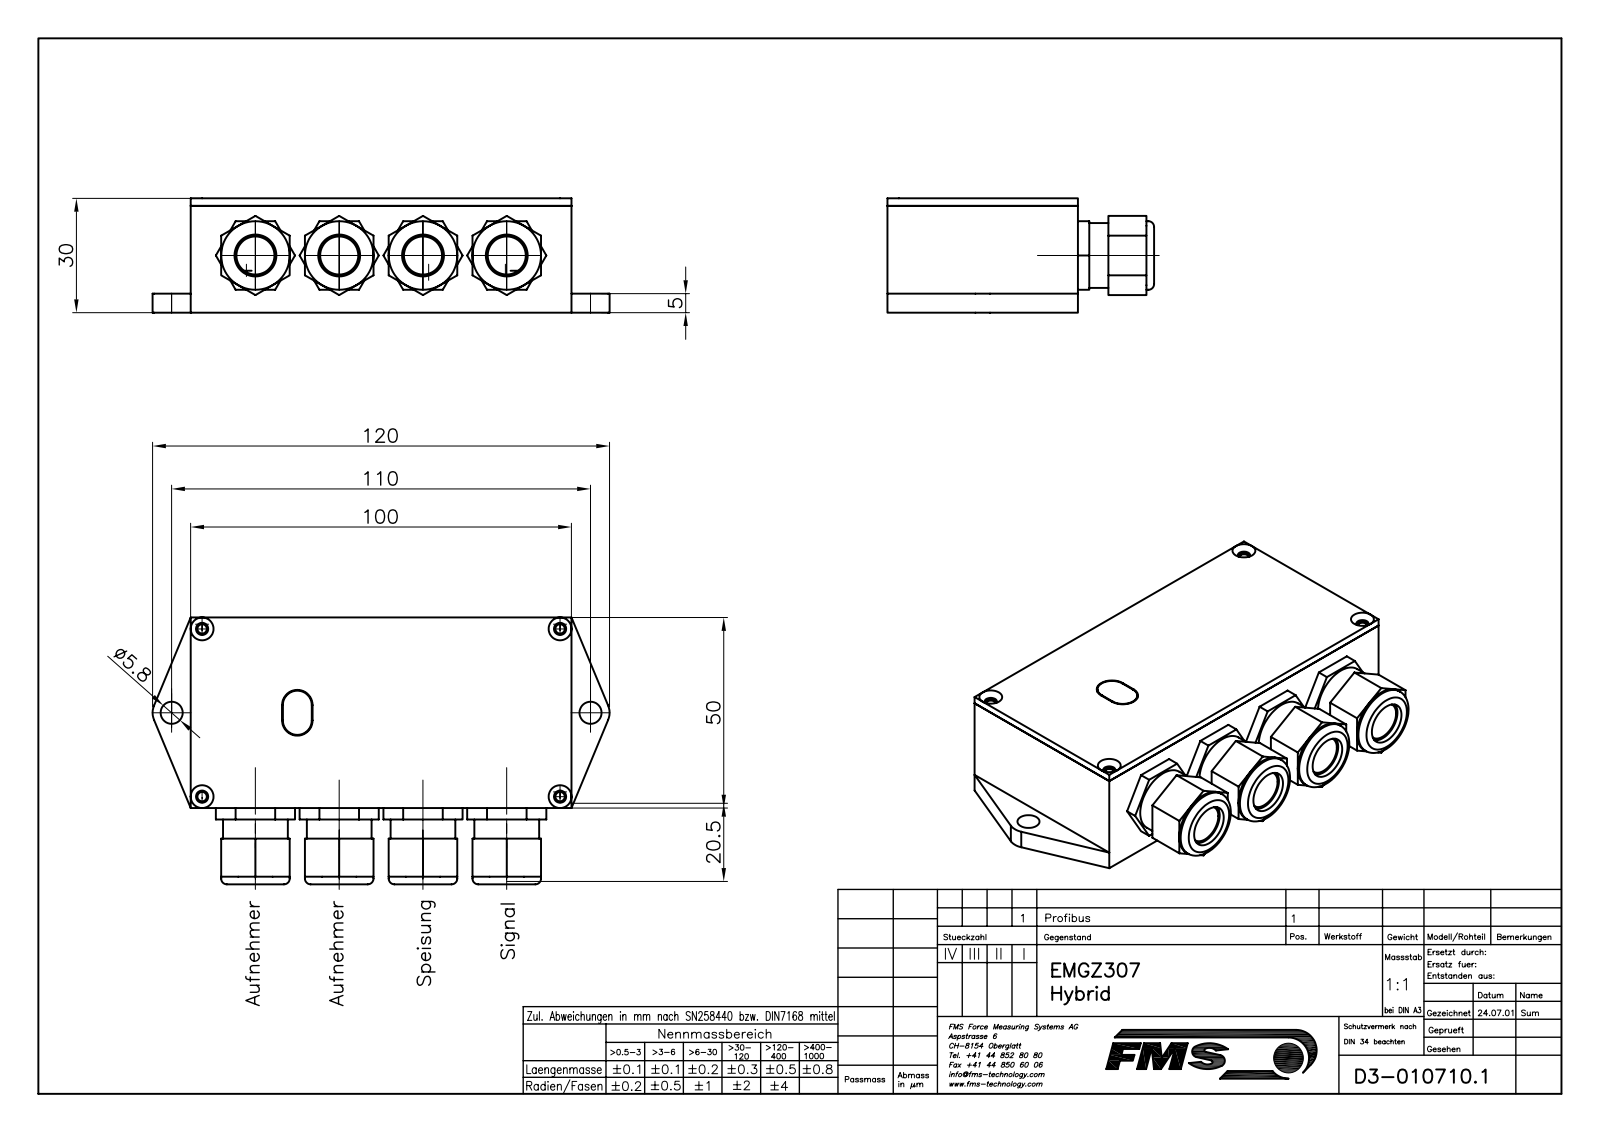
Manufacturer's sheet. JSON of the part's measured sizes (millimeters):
{"part_name": "E0107101; E0107107; E0107102; KABELVERSCHRAUBUNG_M16X1.5 (+8 more)", "step_written_by": "Mechanical Desktop 2009 (CONFIG_CONTROL_DESIGN)", "units": "millimeters", "bodies": {"solids": 15, "faces": 411, "planar": 189, "cylindrical": 154, "other": 68}, "overall_size": [120, 70, 30], "volume_mm3": 77841, "surface_area_mm2": 58560, "round_holes": [[2.46, 4], [3.2, 4], [10, 4], [11, 4], [12, 4], [13.5, 4], [13.9, 4], [16.15, 4], [2, 2], [5.8, 2]], "round_bosses_or_shafts": [[18, 4], [17, 4], [16, 4], [15.5, 4], [3, 1]], "partial_cylinders_radius": [[5, 22], [1, 4], [3.7, 4], [3, 2], [3.8, 2], [4, 2]], "face_to_face_distances": [2, 28, 30, 3, 25, 4, 6, 44, 27, 26], "hole_center_spacings": [23.41, 44, 104.35, 22, 8.9, 20.18, 37.41, 88.78]}
